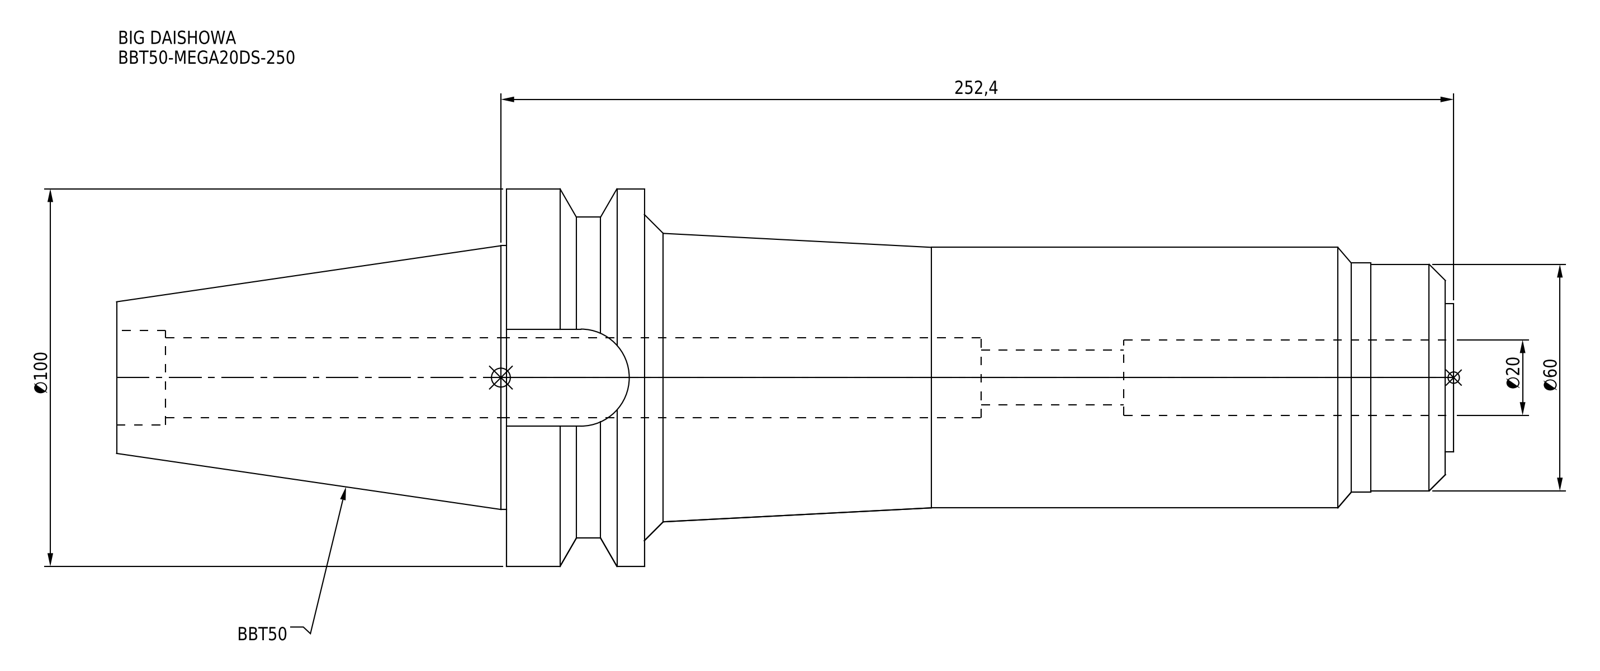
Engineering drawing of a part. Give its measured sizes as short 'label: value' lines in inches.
name: BBT50-MEGA20DS-250
written by: CREO PARAMETRIC BY PTC INC, 2016380 (AUTOMOTIVE_DESIGN)
unit: in
bodies: 1 solid, 57 faces (15 planar, 28 cylindrical, 14 other)
size: 13.945 × 3.937 × 3.937
volume: 72.62 in³; area: 173.1 in²
holes: 1× ⌀0.571, 1× ⌀0.787, 1× ⌀0.835, 1× ⌀0.984
bosses: 1× ⌀3.937, 1× ⌀3.346, 1× ⌀2.75, 1× ⌀2.717, 1× ⌀2.39, 1× ⌀2.362, 1× ⌀1.547
rounds: 1× R0.506
face distances: 1.437, 8.441, 9.878, 0.087, 8.354, 9.791, 13.945, 13.858, 5.504, 4.067
